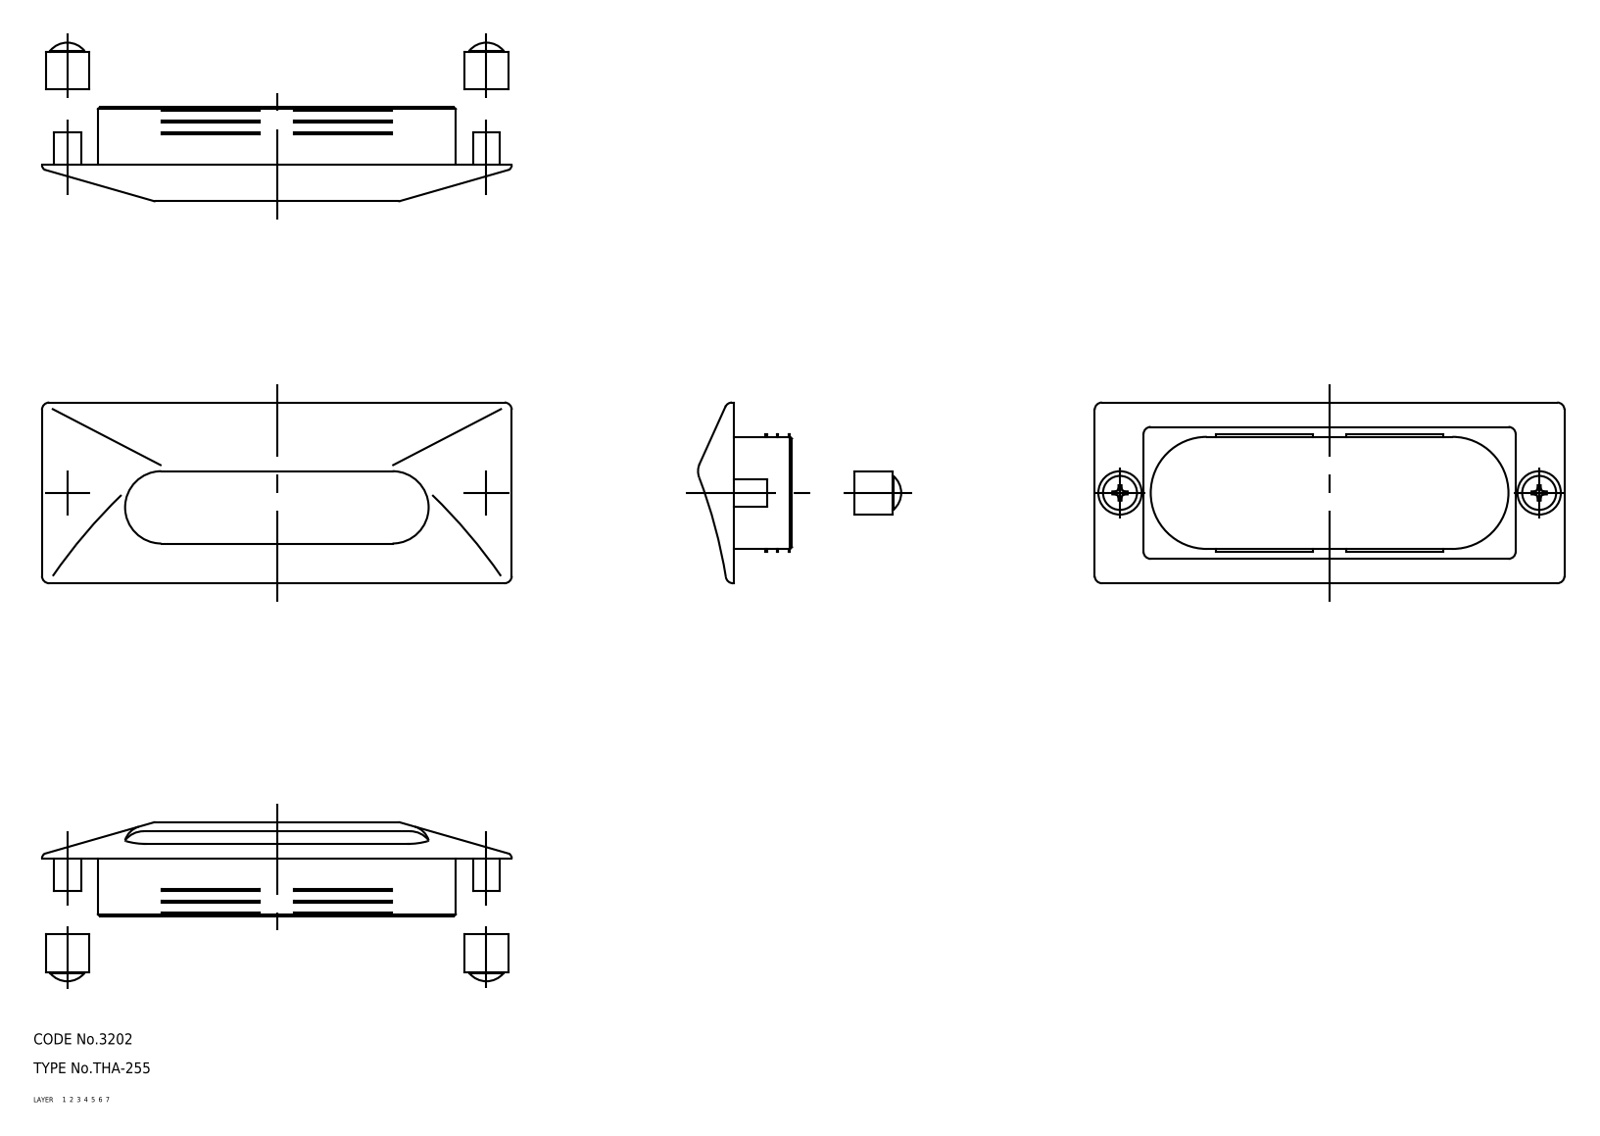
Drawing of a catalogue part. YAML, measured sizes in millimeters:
part_name: "screw; spacer; cover; base (+1 more)"
step_written_by: "CADfix (AUTOMOTIVE_DESIGN)"
units: millimeters
bodies: {solids: 6, faces: 217, planar: 0, cylindrical: 0, other: 217}
overall_size: [130, 50, 26]
volume: 29352
surface_area: 30330
